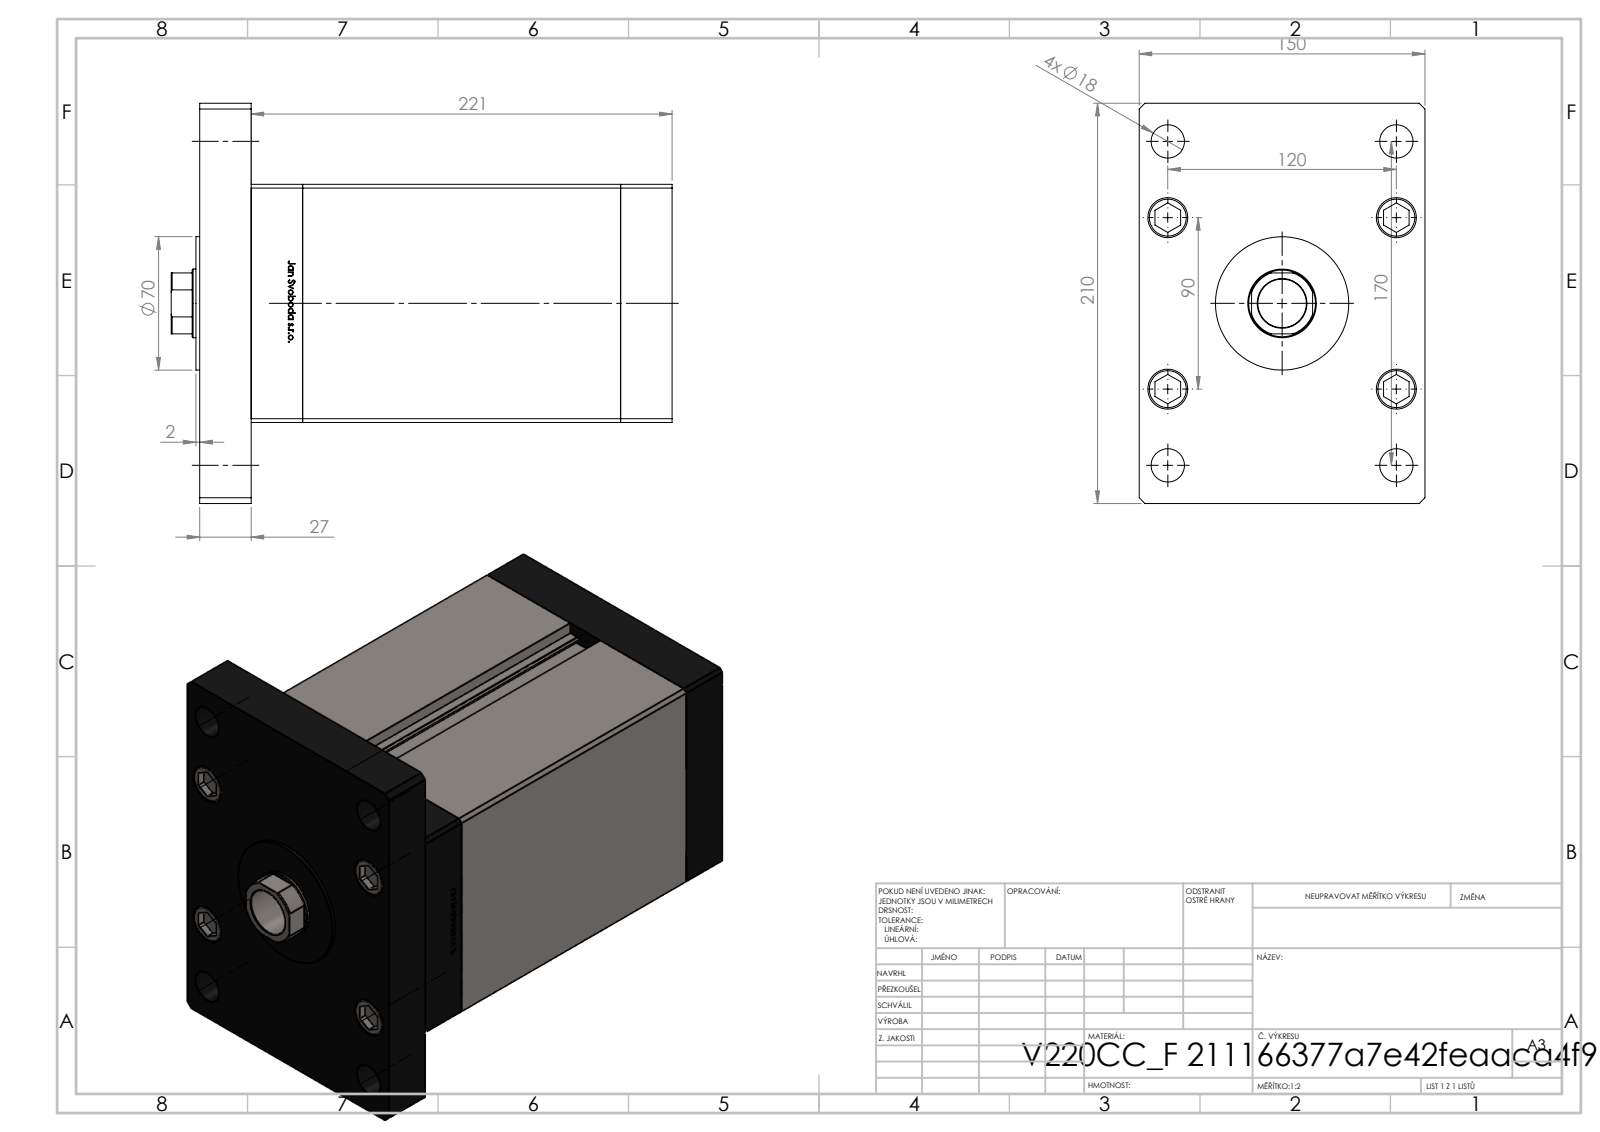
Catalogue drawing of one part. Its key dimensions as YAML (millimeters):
part_name: "V220C BACK_F; V220C_F; V220C_F_MIDDLE; V220C_VC_F (+2 more)"
step_written_by: "SolidWorks 2019 (CONFIG_CONTROL_DESIGN)"
units: millimeters
bodies: {solids: 19, faces: 1298, planar: 513, cylindrical: 179, other: 606}
overall_size: [263, 210, 150]
volume: 4367000
surface_area: 470795
round_holes:
  - {diameter: 17.5, count: 9}
  - {diameter: 22, count: 5}
  - {diameter: 16, count: 4}
  - {diameter: 21, count: 4}
  - {diameter: 25.5, count: 1}
  - {diameter: 36, count: 1}
  - {diameter: 37.5, count: 1}
round_bosses_or_shafts:
  - {diameter: 8, count: 9}
  - {diameter: 21, count: 5}
  - {diameter: 80, count: 1}
  - {diameter: 70, count: 1}
partial_cylinders:
  - {radius: 0.93, count: 2}
  - {radius: 17.5, count: 1}
face_to_face_distances: [27, 194, 221, 150, 125, 167, 54, 248, 33.5, 6.5]
hole_center_spacings: [51, 40, 75, 104.04, 120, 126.49, 130, 176.92]
